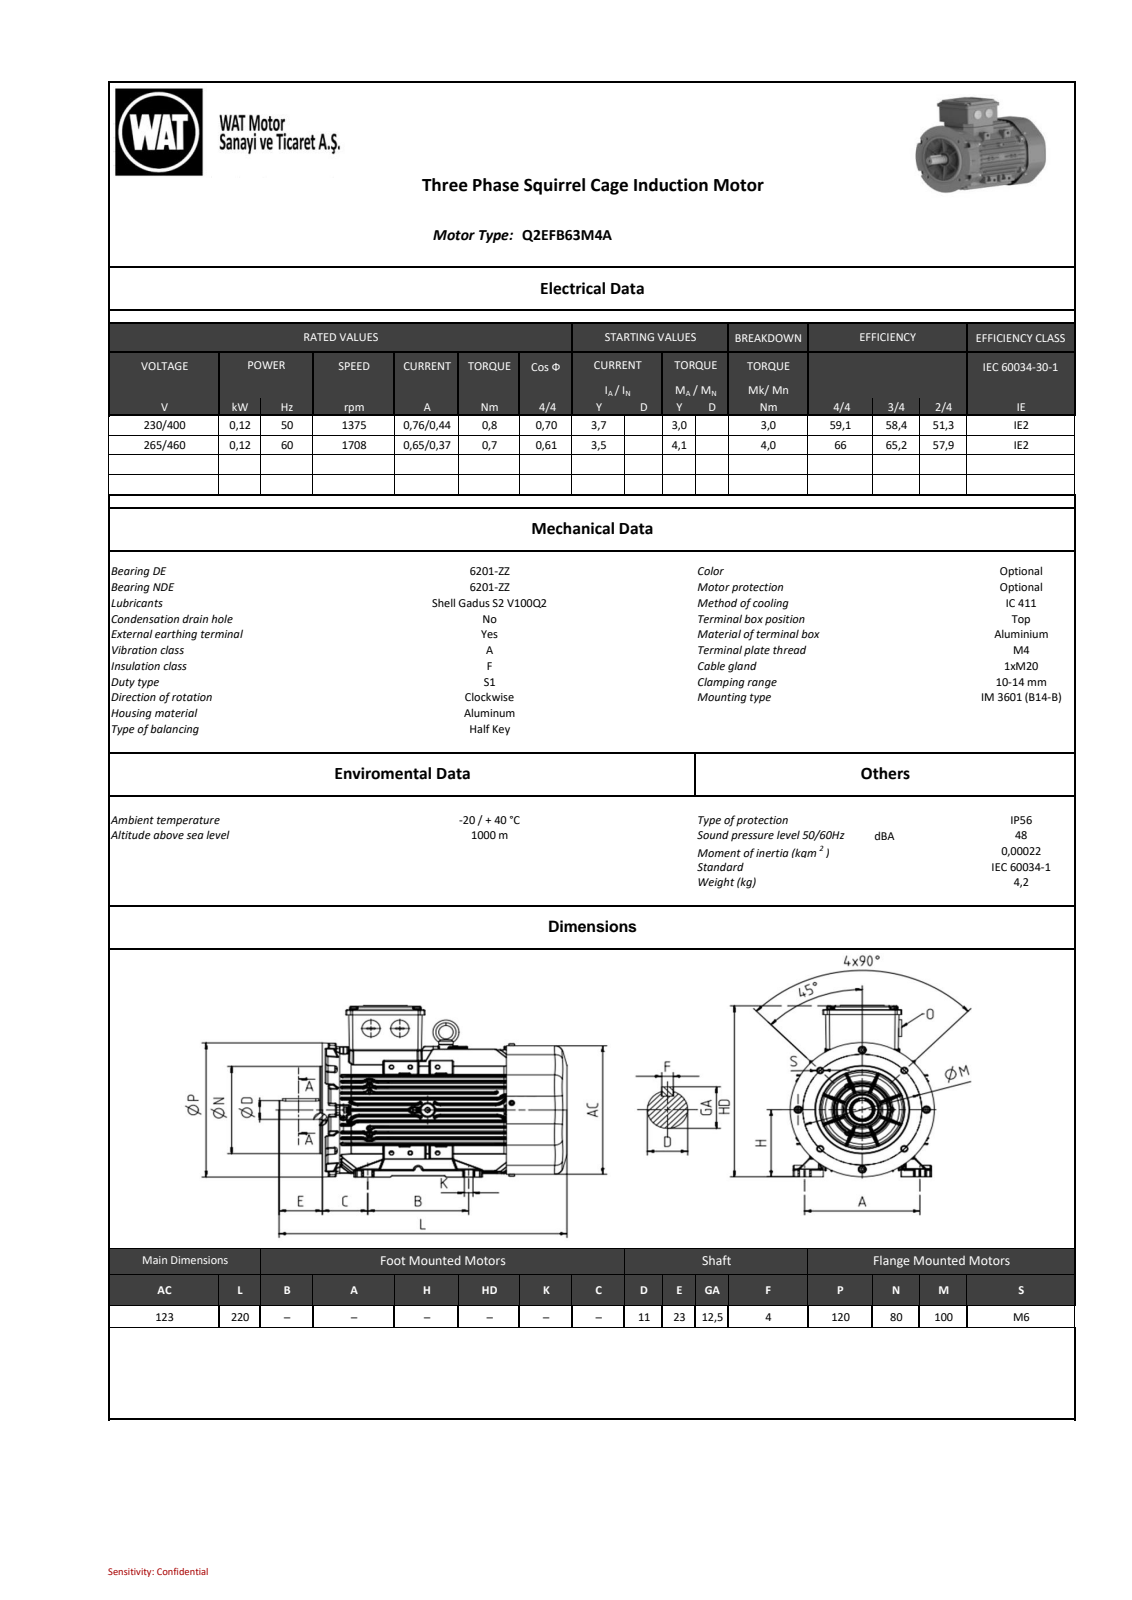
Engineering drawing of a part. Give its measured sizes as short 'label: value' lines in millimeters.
name: QSFB63GMM
written by: UNIX (AUTOMOTIVE_DESIGN)
unit: mm
bodies: 5 solids, 2704 faces (0 planar, 0 cylindrical, 2704 other)
size: 219.5 × 159.6 × 128
volume: 27 193 mm³; area: 373 233 mm²
